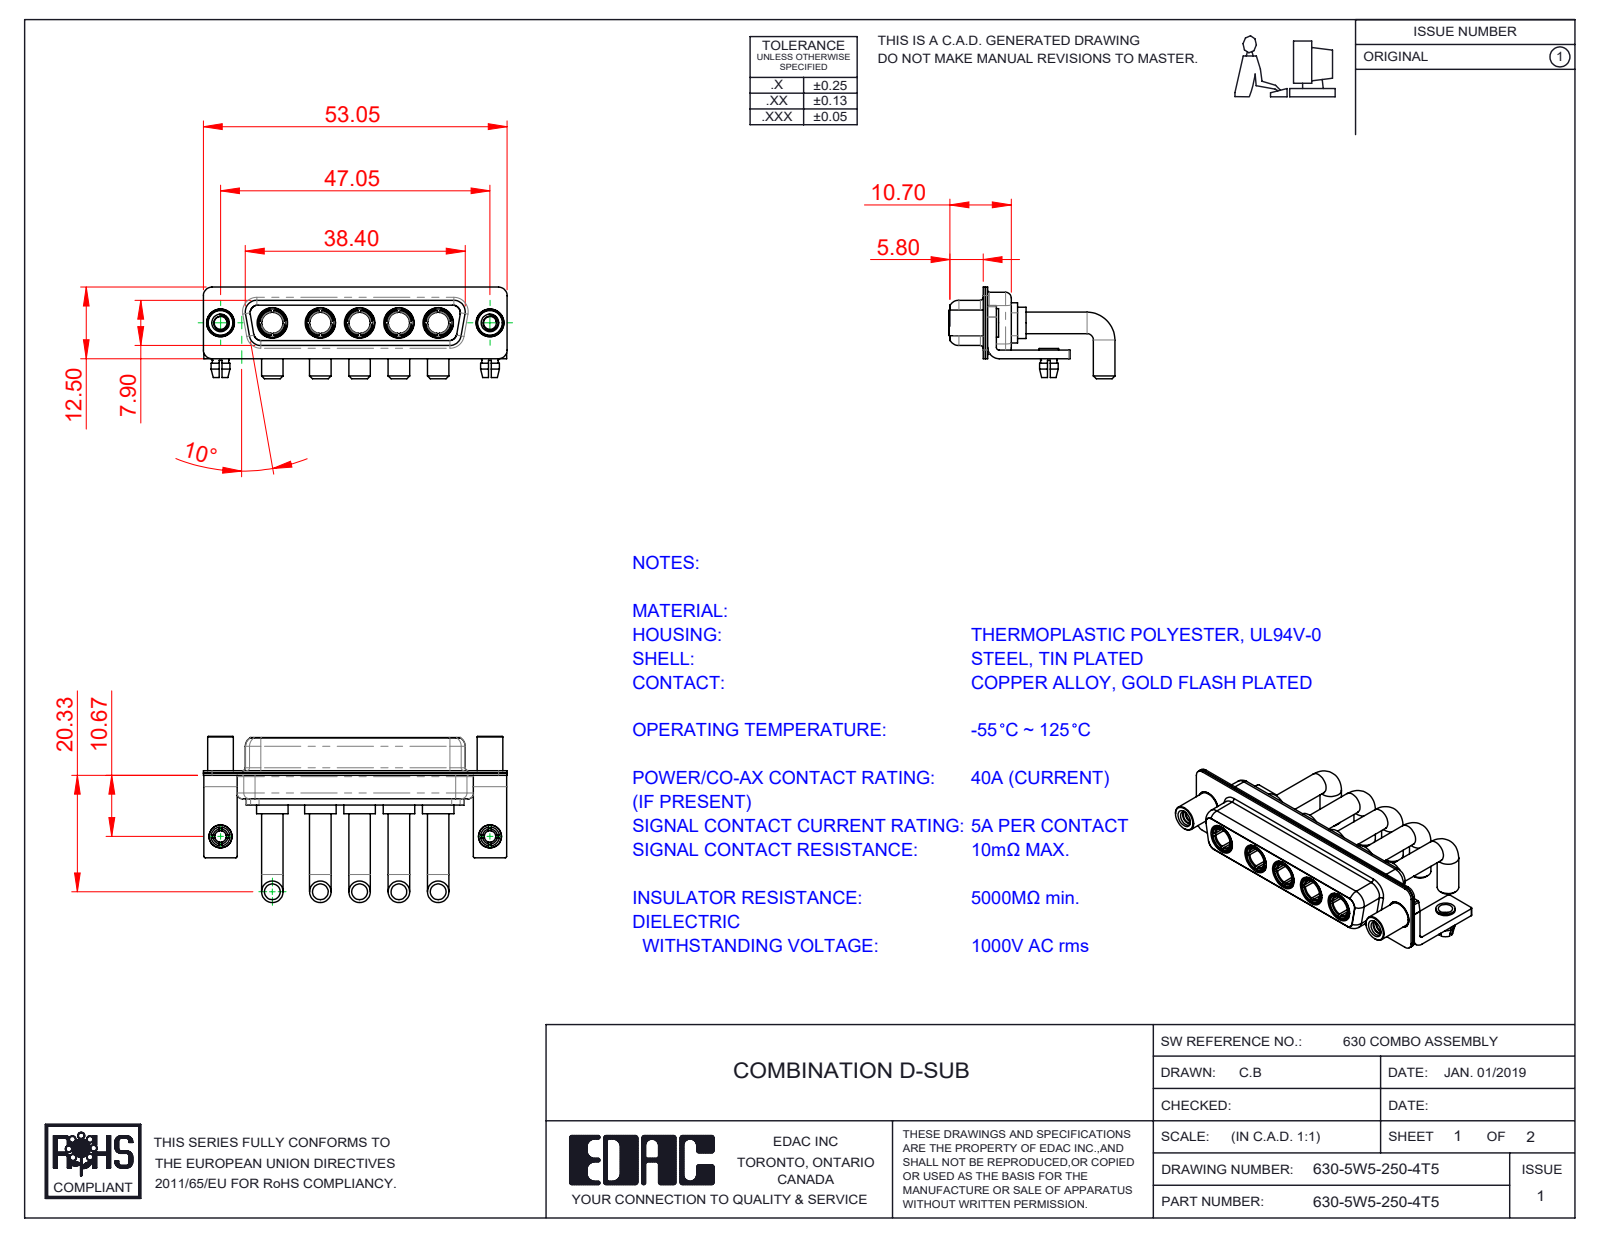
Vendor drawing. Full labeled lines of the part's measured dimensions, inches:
Part name (STEP PRODUCT): 630Combo Shell Rear_25 Contacts; 630-5W5-250-4T5; 630Combo Stabilizer Bracket; Power Socket_Ext 40A RA (+4 more)
STEP written by: SolidWorks 2020 (CONFIG_CONTROL_DESIGN)
Units: inches
Bodies: 19 solids, 849 faces (282 planar, 354 cylindrical, 213 other)
Overall size (bounding box): 2.089 × 1.142 × 0.63
Volume: 0.318 in³ · Surface area: 16.2 in²
Round holes (diameter × count): ⌀0.191 ×7, ⌀0.146 ×5, ⌀0.209 ×5, ⌀0.079 ×2, ⌀0.089 ×2, ⌀0.098 ×2, ⌀0.126 ×2, ⌀0.157 ×2, ⌀0.159 ×2
Round bosses / shafts (diameter × count): ⌀0.148 ×10, ⌀0.217 ×5, ⌀0.205 ×5, ⌀0.195 ×5, ⌀0.187 ×5, ⌀0.197 ×2, ⌀0.195 ×2, ⌀0.189 ×2
Partial cylindrical surfaces — rounded edges, fillets, slot ends (radius × count): R0.01 ×16, R0.059 ×16, R0.079 ×13, R0.053 ×8, R0.063 ×8, R0.02 ×5, R0.083 ×5, R0.024 ×4
Main face-to-face distances: 0.016, 0.018, 0.055, 0.333, 0.071, 0.031, 0.35, 0.244, 0.059, 0.278
Hole centre spacings: 0.27, 0.356, 1.496, 1.852, 0.27, 0.33, 0.54, 0.541
